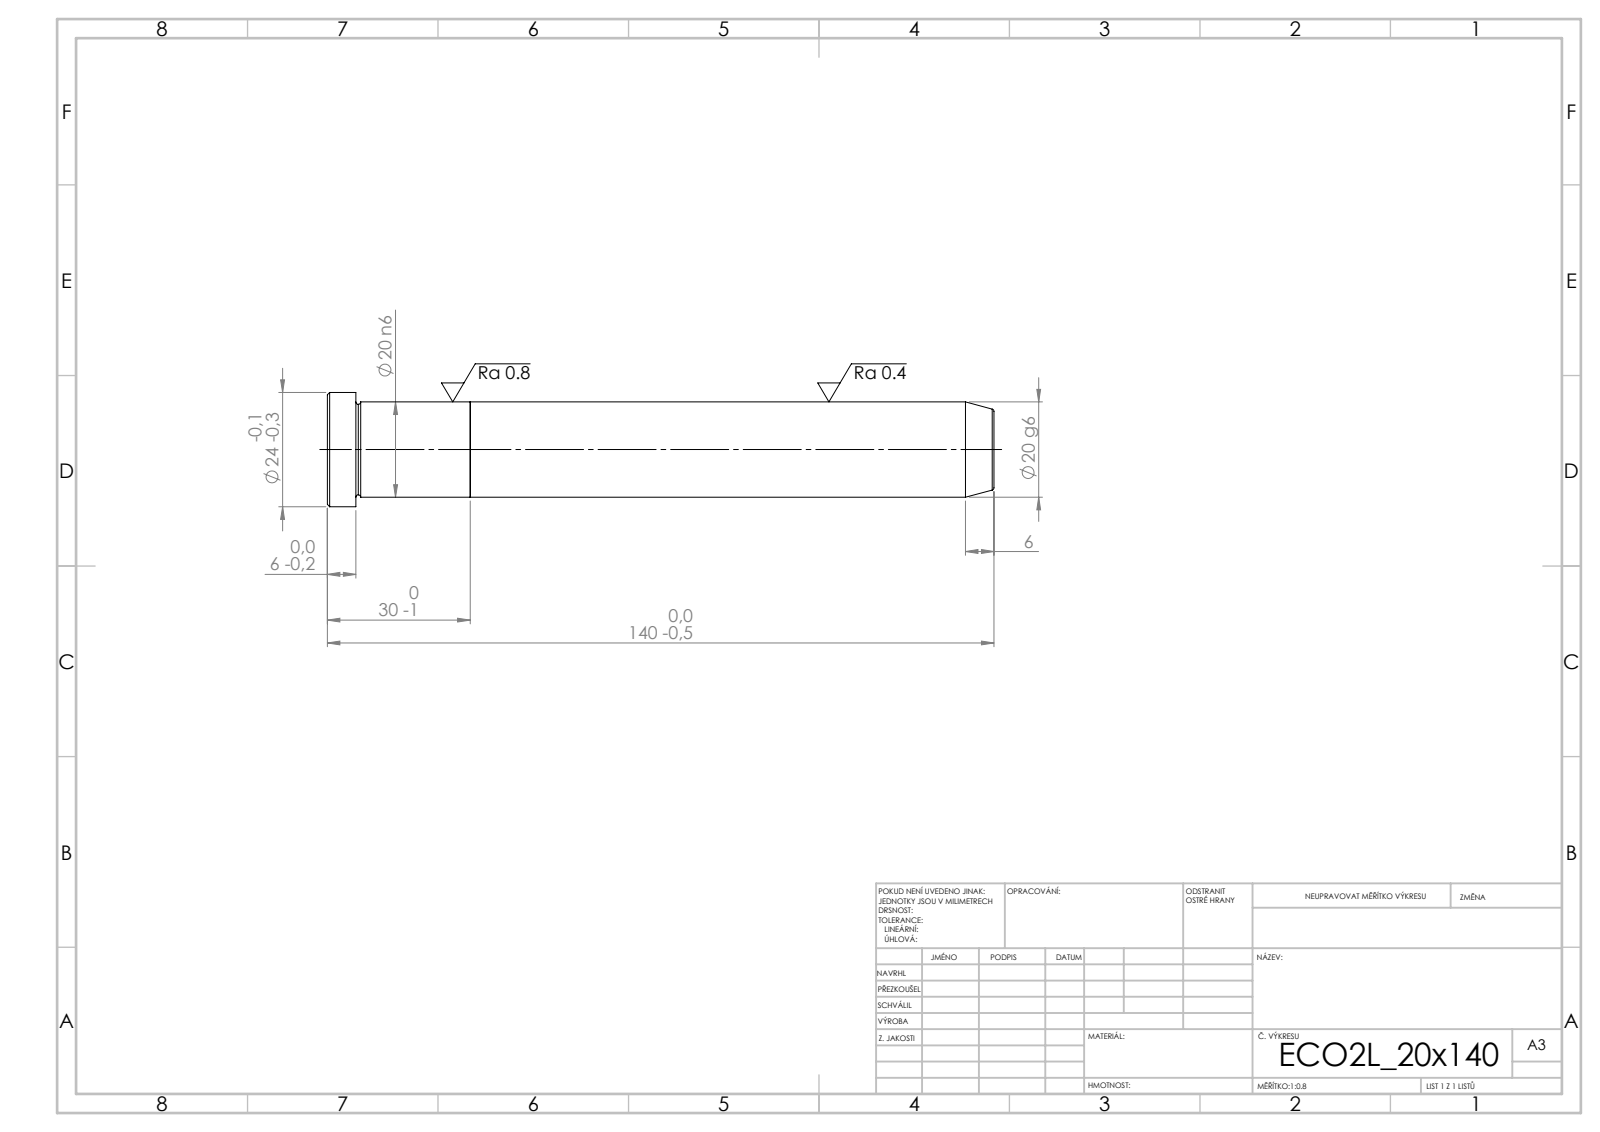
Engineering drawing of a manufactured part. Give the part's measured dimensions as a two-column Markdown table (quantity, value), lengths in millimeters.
| quantity | value |
| --- | --- |
| STEP written by | SolidWorks 2019 (CONFIG_CONTROL_DESIGN) |
| units | millimeters |
| bodies | 2 solids, 21 faces (5 planar, 6 cylindrical, 10 other) |
| overall size | 140 × 24 × 24 |
| volume | 44 490 mm³ |
| surface area | 10 298 mm² |
| round bosses / shafts (diameter × count) | 24 × 1, 20 × 1 |
| main face-to-face distances | 30, 110, 140, 134, 24, 6 |
